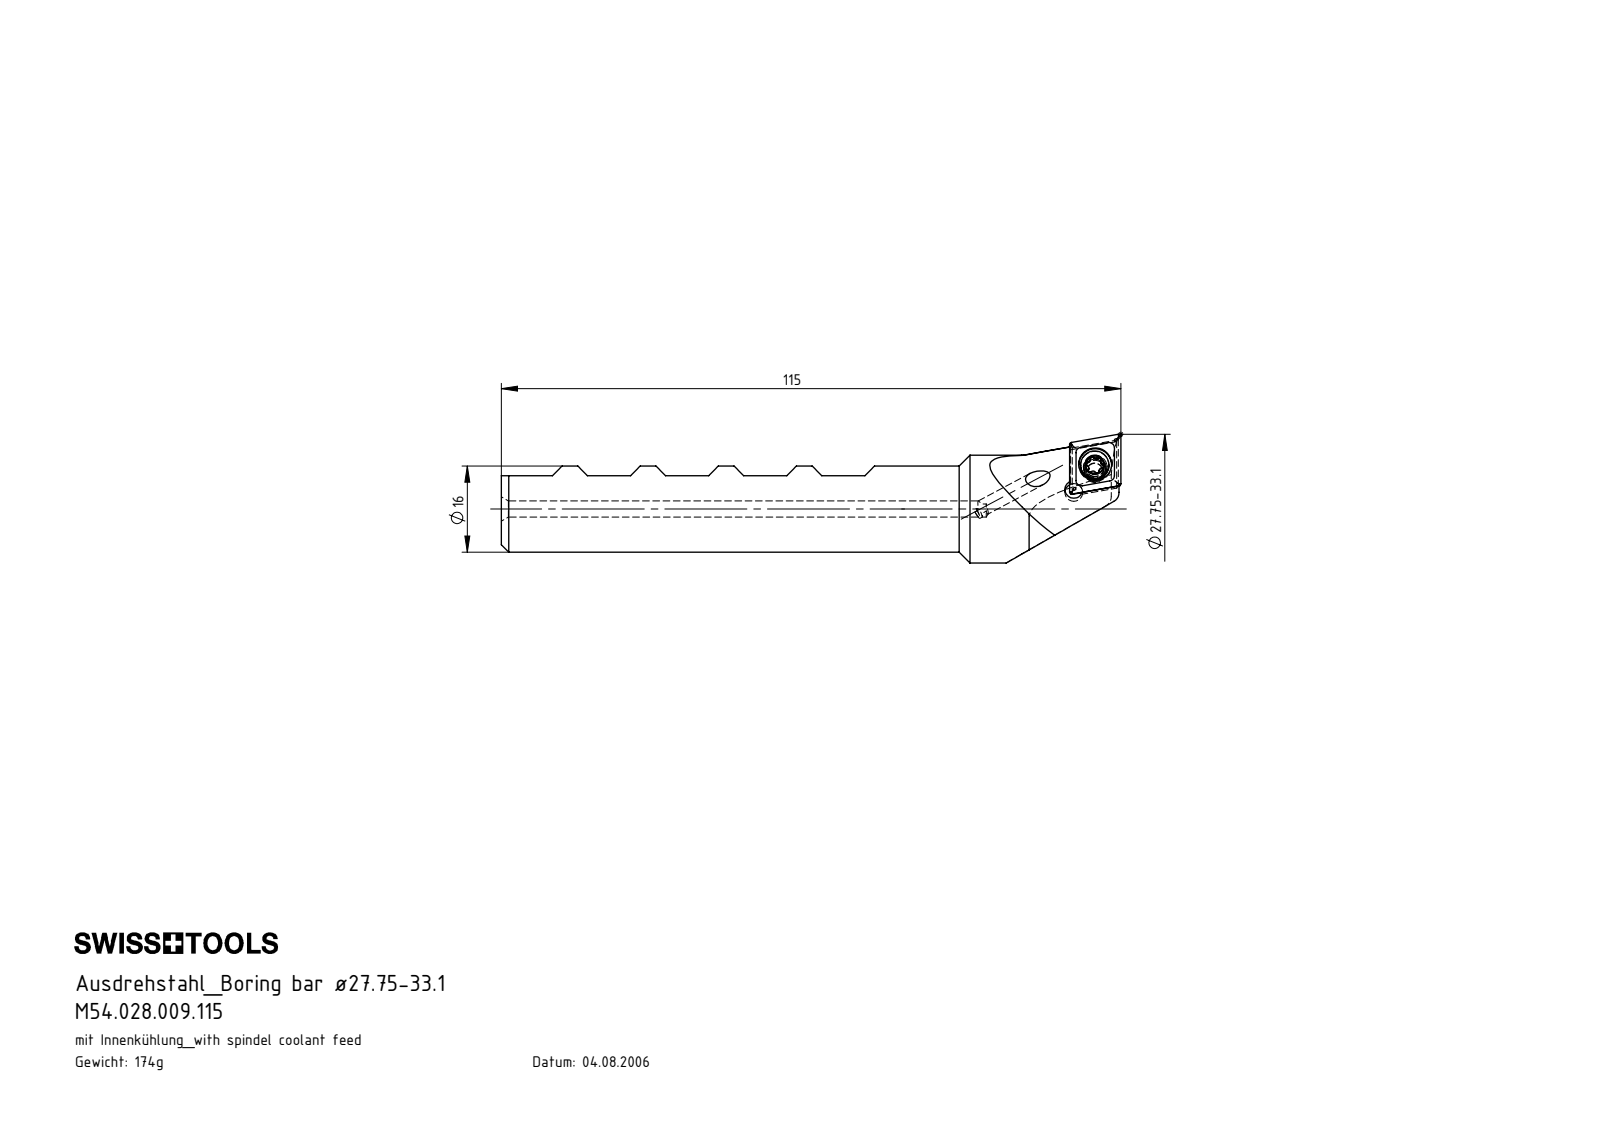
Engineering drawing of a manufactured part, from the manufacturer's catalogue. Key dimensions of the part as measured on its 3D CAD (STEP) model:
Part name (STEP PRODUCT): B28-WCB.K11.115_A; CCMT09T304; WCB-ER2.001.009_A; B28.WCB.K11.115
STEP written by: SolidWorks 2017 (AUTOMOTIVE_DESIGN)
Units: millimetres
Bodies: 3 solids, 118 faces (45 planar, 27 cylindrical, 46 other)
Overall size (bounding box): 115 × 23.88 × 21.36
Volume: 22 164 mm³ · Surface area: 7 783 mm²
Round holes (diameter × count): ⌀3 ×2, ⌀3.3 ×2, ⌀4.4 ×1, ⌀6.1 ×1
Round bosses / shafts (diameter × count): ⌀20 ×1, ⌀16 ×1, ⌀5.25 ×1, ⌀4 ×1
Partial cylindrical surfaces — rounded edges, fillets, slot ends (radius × count): R0.34 ×6, R0.59 ×6, R2 ×1, R10.2 ×1, R12 ×1
Main face-to-face distances: 10.25, 8.16, 20.5, 20.51, 30.76, 11.93, 3.77, 12.13, 3.97, 30.75
Hole centre spacings: 6.07, 6.19
